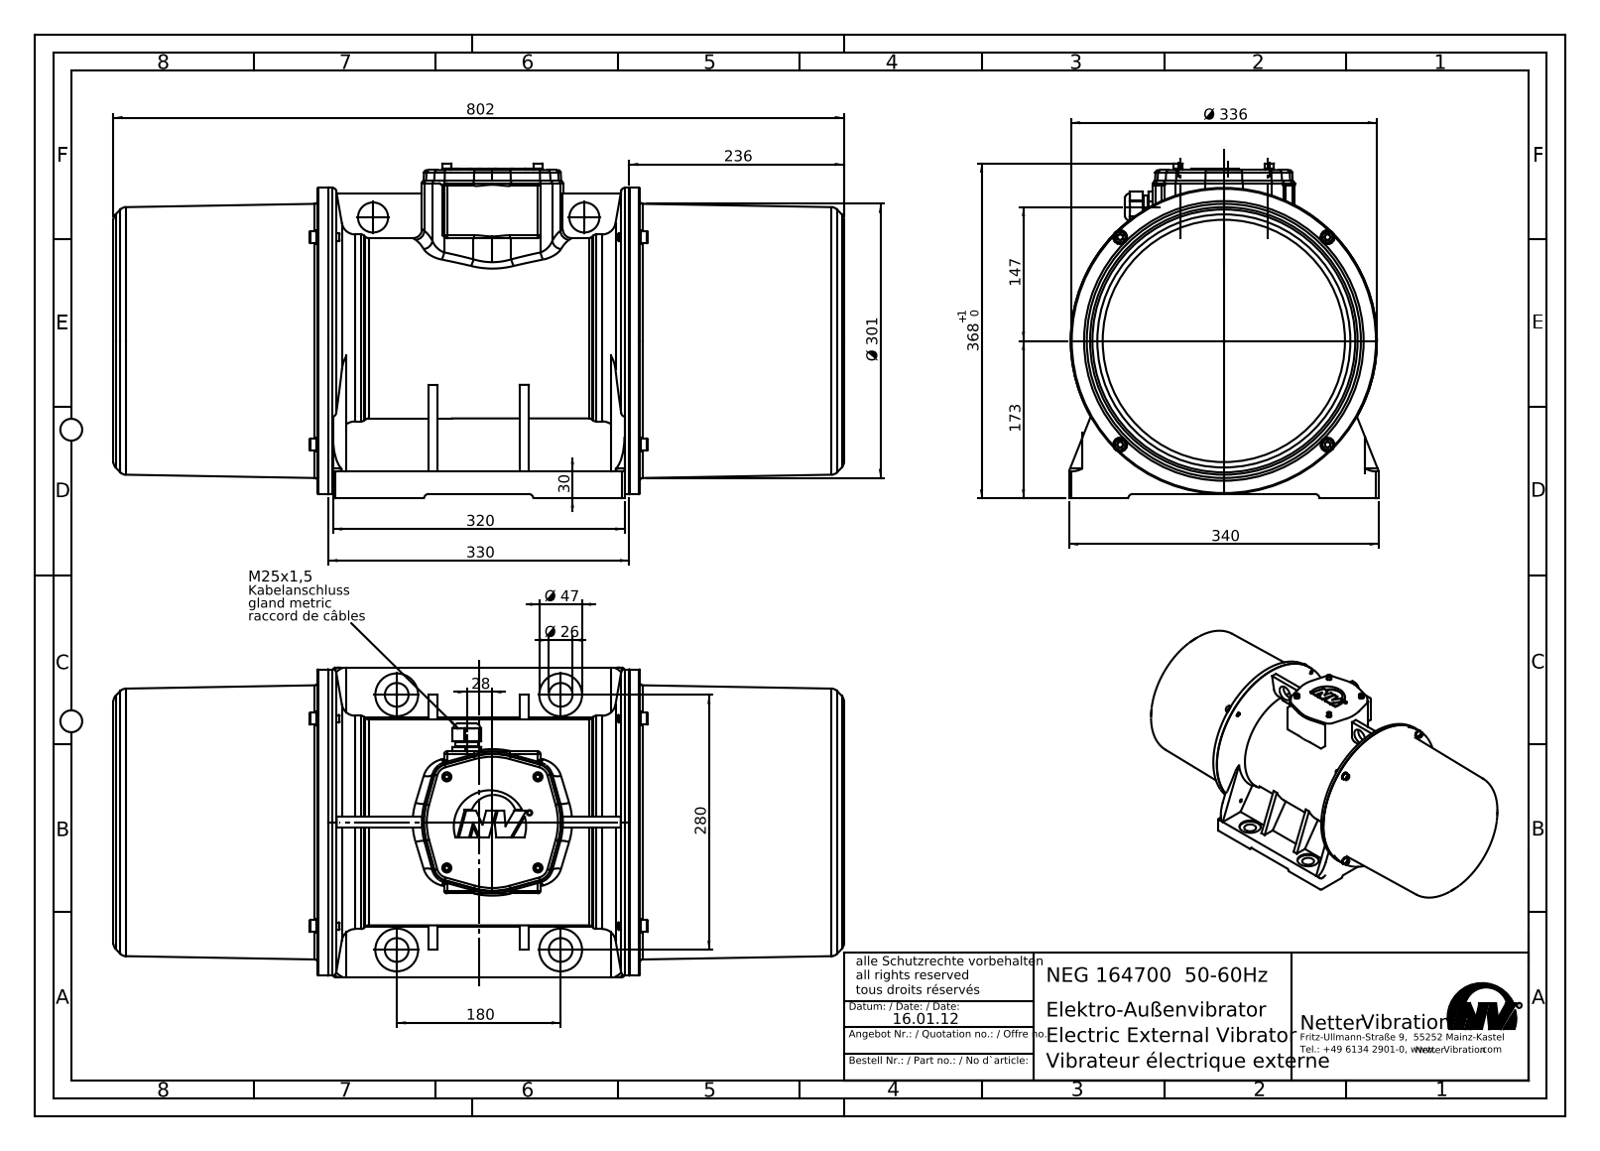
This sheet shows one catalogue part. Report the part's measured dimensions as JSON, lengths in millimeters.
{"part_name": "NEG 164700 50-60Hz", "step_written_by": "SolidWorks 2010 (AUTOMOTIVE_DESIGN)", "units": "millimeters", "bodies": {"solids": 2, "faces": 1934, "planar": 978, "cylindrical": 283, "other": 673}, "overall_size": [802, 367.75, 340], "volume_mm3": 13980000, "surface_area_mm2": 2158000, "round_holes": [[6.5, 4], [6.8, 4], [8.4, 4], [9, 4], [26, 4], [47, 4], [33, 2], [4.5, 1], [20, 1], [23.5, 1], [272, 1], [276, 1]], "round_bosses_or_shafts": [[6, 5], [15, 4], [13, 4], [10, 4], [8, 4], [336, 1], [292, 1], [25, 1]], "partial_cylinders_radius": [[3, 35], [0.5, 30], [5, 4], [15, 4], [18.5, 2], [18.5, 2], [25.6, 1], [39.7, 1]], "face_to_face_distances": [4.5, 797.5, 793, 802, 5, 25, 236, 566, 231.5, 561.5], "hole_center_spacings": [100, 160.99, 227.68, 93.41, 105.48, 141.42, 154.03, 179.23]}
